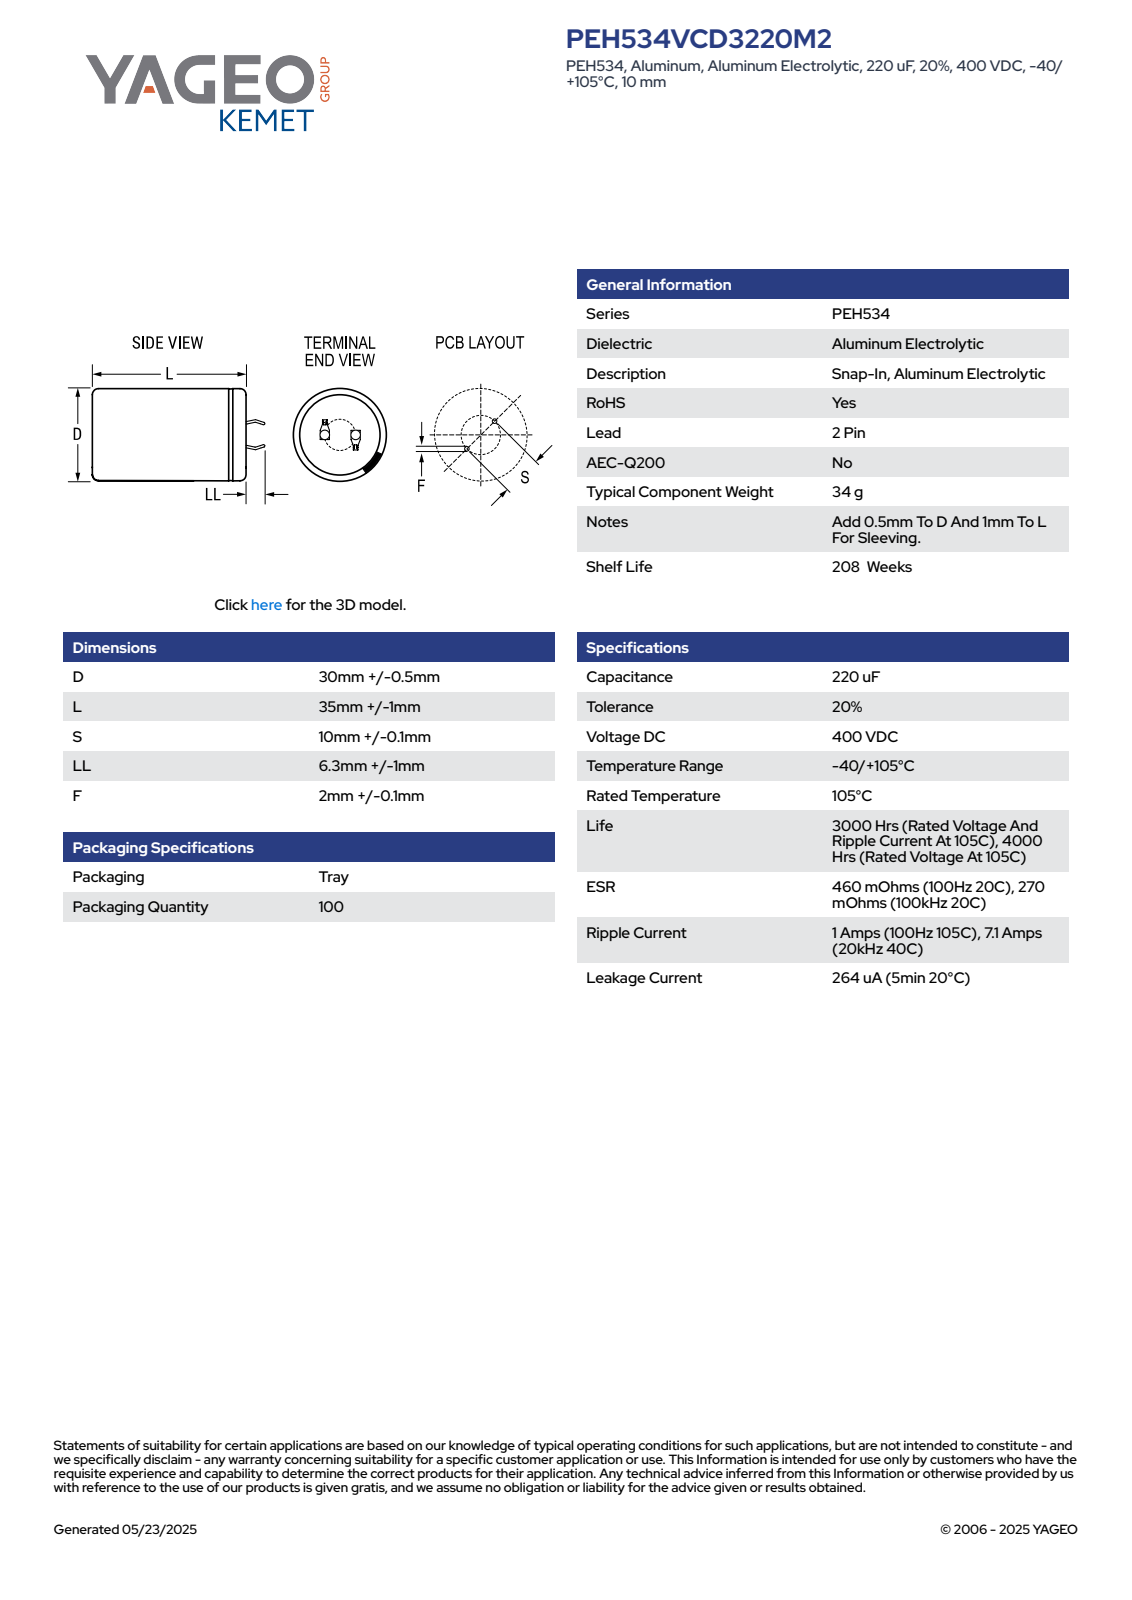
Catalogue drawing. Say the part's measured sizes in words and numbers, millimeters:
The part is named "CARS_K2P_30X35_D30.5L36S10LL7.3F2.1". Its 3-D file was written by "SolidWorks 2014 (AUTOMOTIVE_DESIGN)". It is 1 solid with 100 faces: 52 planar, 9 cylindrical and 39 other. Overall it measures 43.29 by 30.5 by 30.5 millimeters. Its volume is 25 985 cubic millimeters and its surface area 4 922 square millimeters. Round holes: 1 of diameter 26.99. Round bosses or shafts: 1 of diameter 30.5. Partial cylindrical surfaces (rounded edges, fillets, slot ends): 1 of radius 15.24. The main face-to-face distances are 35.99, 0.6, 36.49, 0.5, 7.08, 7.64, 0.75, 1.35, 7.68, 6.48.
